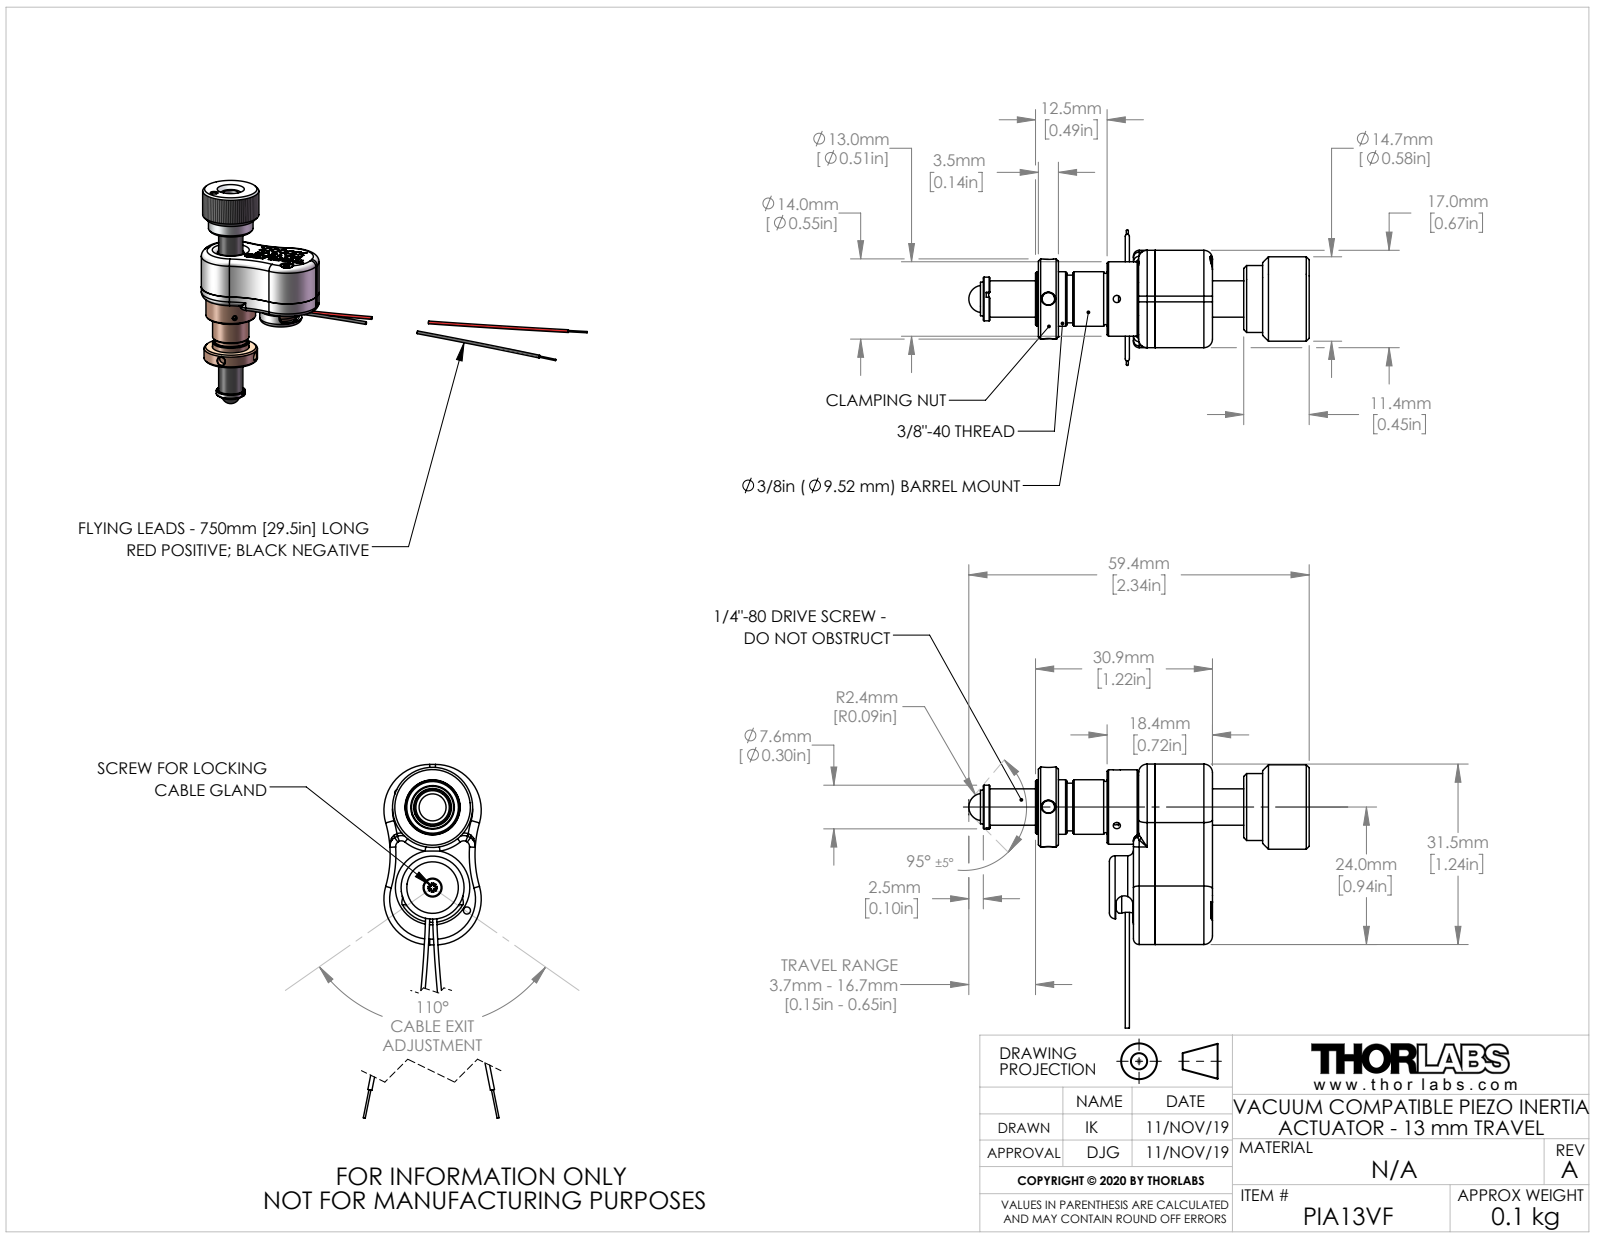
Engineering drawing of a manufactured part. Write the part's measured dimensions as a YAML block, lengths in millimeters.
part_name: "PIA13VF1.STEP; PIA13VF9.STEP; PIA13VF15.STEP; PIA13VF (+8 more)"
step_written_by: "SolidWorks 2019 (AUTOMOTIVE_DESIGN)"
units: millimeters
bodies: {solids: 16, faces: 893, planar: 360, cylindrical: 276, other: 257}
overall_size: [102.82, 59.44, 23.71]
volume: 6402
surface_area: 8694
round_holes:
  - {diameter: 1.25, count: 9}
  - {diameter: 1.8, count: 3}
  - {diameter: 2.2, count: 3}
  - {diameter: 1.42, count: 2}
  - {diameter: 2, count: 2}
  - {diameter: 2.5, count: 2}
  - {diameter: 0.8, count: 1}
  - {diameter: 3.2, count: 1}
  - {diameter: 3.4, count: 1}
  - {diameter: 3.9, count: 1}
  - {diameter: 6.04, count: 1}
  - {diameter: 6.22, count: 1}
round_bosses_or_shafts:
  - {diameter: 3, count: 3}
  - {diameter: 1.6, count: 3}
  - {diameter: 0.35, count: 2}
  - {diameter: 14.73, count: 1}
  - {diameter: 14, count: 1}
  - {diameter: 13, count: 1}
  - {diameter: 11.7, count: 1}
  - {diameter: 11, count: 1}
partial_cylinders:
  - {radius: 0.18, count: 24}
  - {radius: 1, count: 17}
  - {radius: 2, count: 6}
  - {radius: 1.5, count: 5}
  - {radius: 7.2, count: 4}
  - {radius: 7.6, count: 4}
  - {radius: 7.7, count: 4}
  - {radius: 8, count: 4}
face_to_face_distances: [0.8, 12.1, 12.9, 1.9, 10.2, 11, 0.4, 0.7, 3.5, 13.1]
hole_center_spacings: [5, 8.66, 19, 6.5, 12.29, 18.97, 1.85, 2.85]
